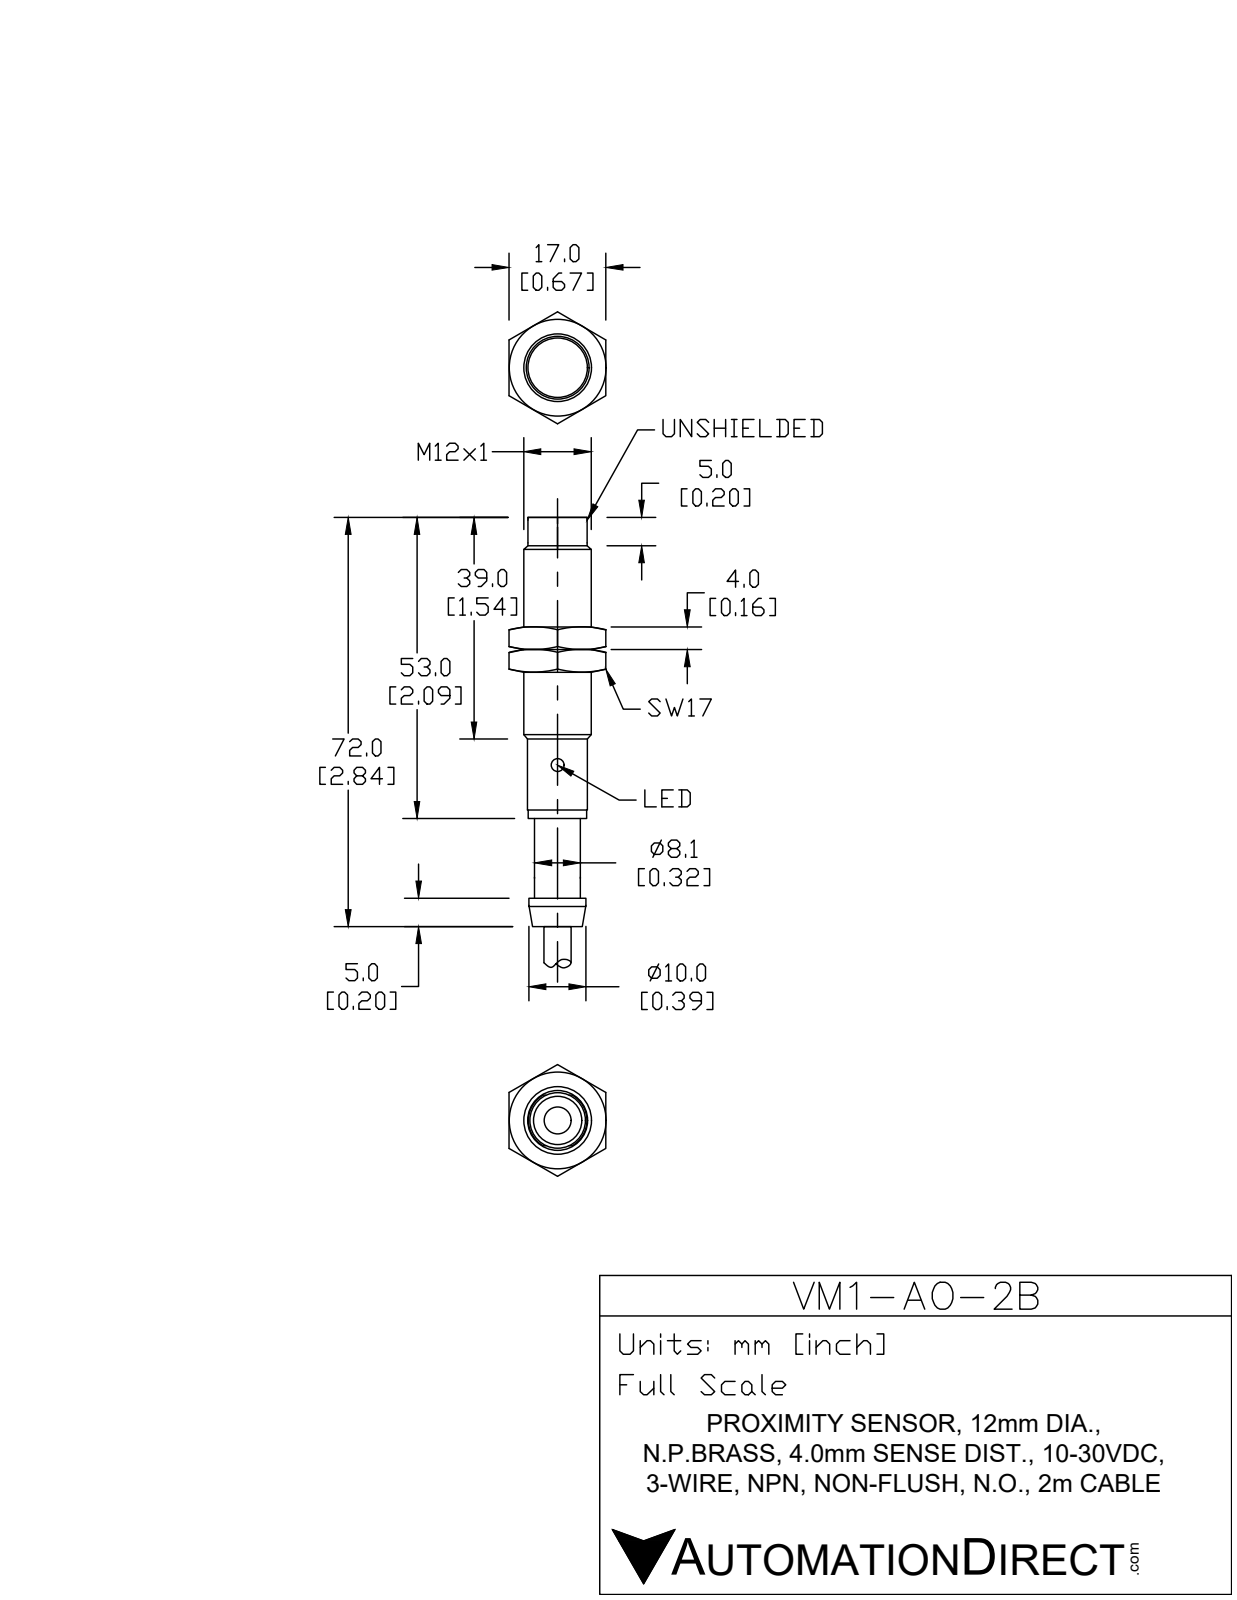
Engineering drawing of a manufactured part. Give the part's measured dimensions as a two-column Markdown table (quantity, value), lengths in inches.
| quantity | value |
| --- | --- |
| part name | VM1-A0-2B |
| STEP written by | SolidWorks 2017 (AUTOMOTIVE_DESIGN) |
| units | inches |
| bodies | 4 solids, 39 faces (11 planar, 14 cylindrical, 14 other) |
| overall size | 3.681 × 0.472 × 0.472 |
| volume | 0.424 in³ |
| surface area | 6.038 in² |
| round holes (diameter × count) | 0.098 × 1, 0.193 × 1 |
| round bosses / shafts (diameter × count) | 0.472 × 1, 0.413 × 1, 0.406 × 1, 0.315 × 1, 0.185 × 1 |
| main face-to-face distances | 1.909, 0.197, 2.106, 2.638, 2.165, 1.969, 0.059, 2.835, 0.728, 0.669 |
